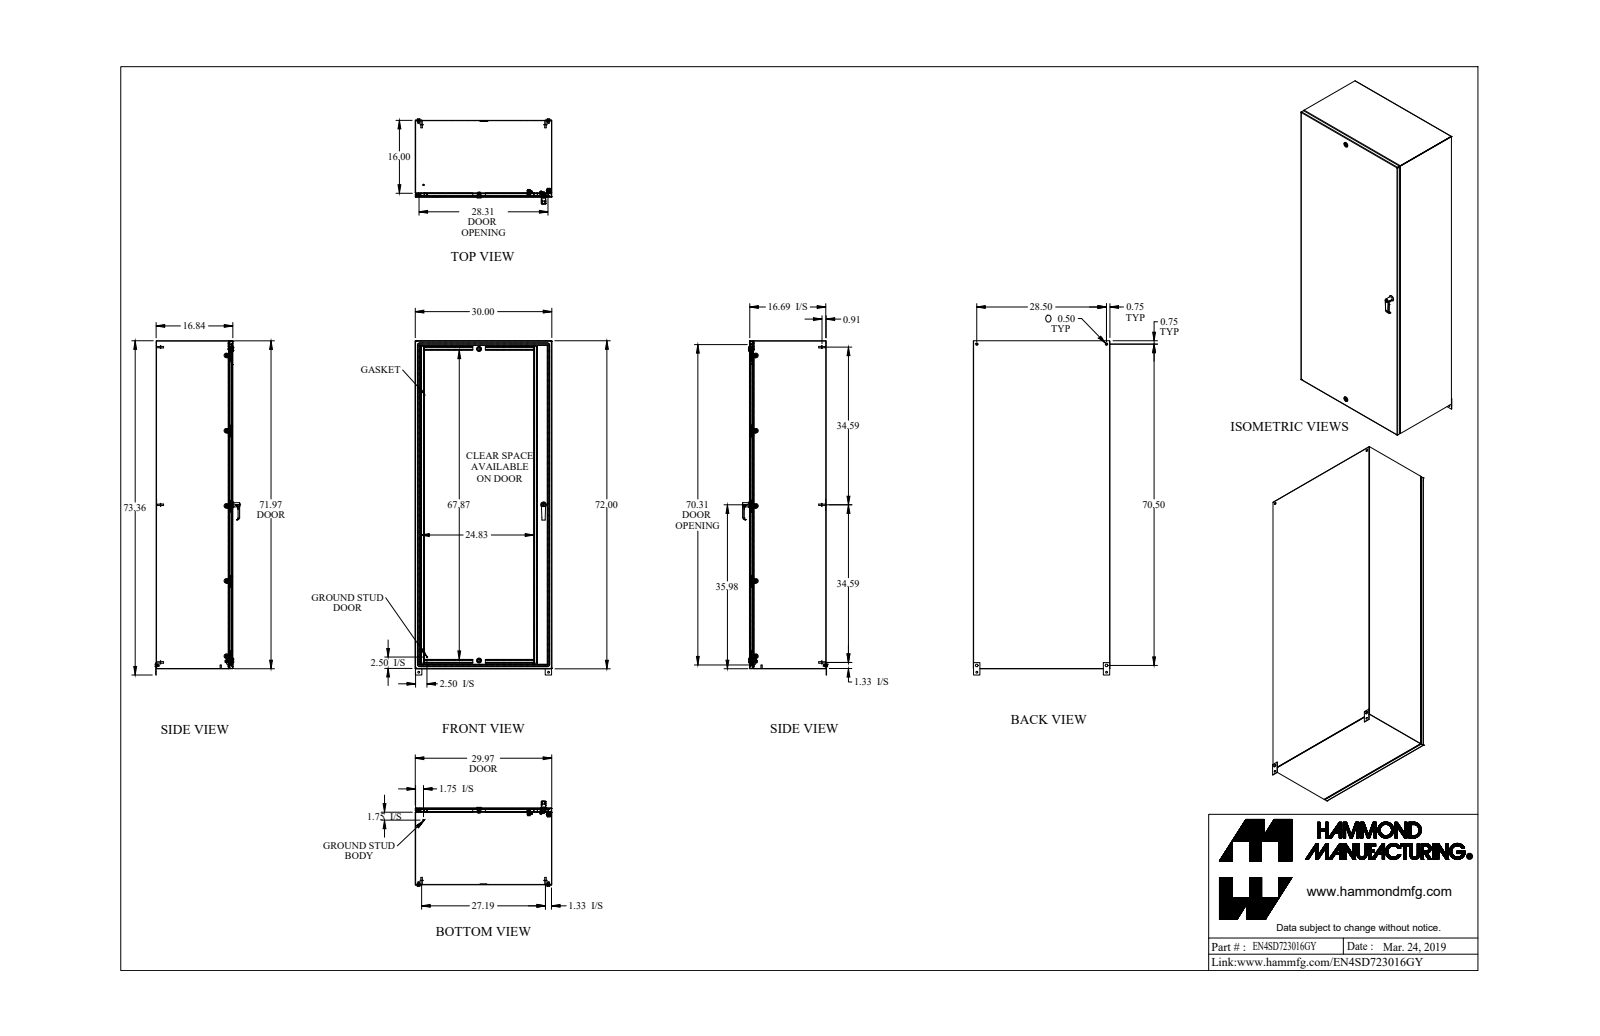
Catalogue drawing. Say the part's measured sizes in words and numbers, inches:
The part is named "EN4SD723016GY". Its 3-D file was written by "SolidWorks 2018 (AUTOMOTIVE_DESIGN)". It is 98 solids with 2429 faces: 1159 planar, 890 cylindrical and 380 other. Overall it measures 73.363 by 30 by 18.693 inches. Its volume is 632.1 cubic inches and its surface area 17 749 square inches. Round holes: 10 of diameter 0.176, 6 of diameter 0.196, 5 of diameter 0.25, 5 of diameter 0.265, 5 of diameter 0.413, 4 of diameter 0.256, 4 of diameter 0.313, 4 of diameter 0.39, 4 of diameter 0.394, 4 of diameter 0.5, 2 of diameter 0.232, 2 of diameter 0.307. Round bosses or shafts: 11 of diameter 0.25, 10 of diameter 0.375, 10 of diameter 0.156, 7 of diameter 0.625, 6 of diameter 0.313, 6 of diameter 0.27, 5 of diameter 1, 4 of diameter 0.63. Partial cylindrical surfaces (rounded edges, fillets, slot ends): 24 of radius 0.043, 19 of radius 0.062, 17 of radius 0.036, 17 of radius 0.108, 15 of radius 0.03, 14 of radius 0.125, 10 of radius 0.006, 10 of radius 0.094. The main face-to-face distances are 0.072, 16.765, 29.928, 16.693, 16.837, 29.856, 30, 71.928, 71.856, 72. The hole center spacings are 16.513, 28.5, 49.487, 0.787, 1.5, 13.313, 14.208, 15.267.
